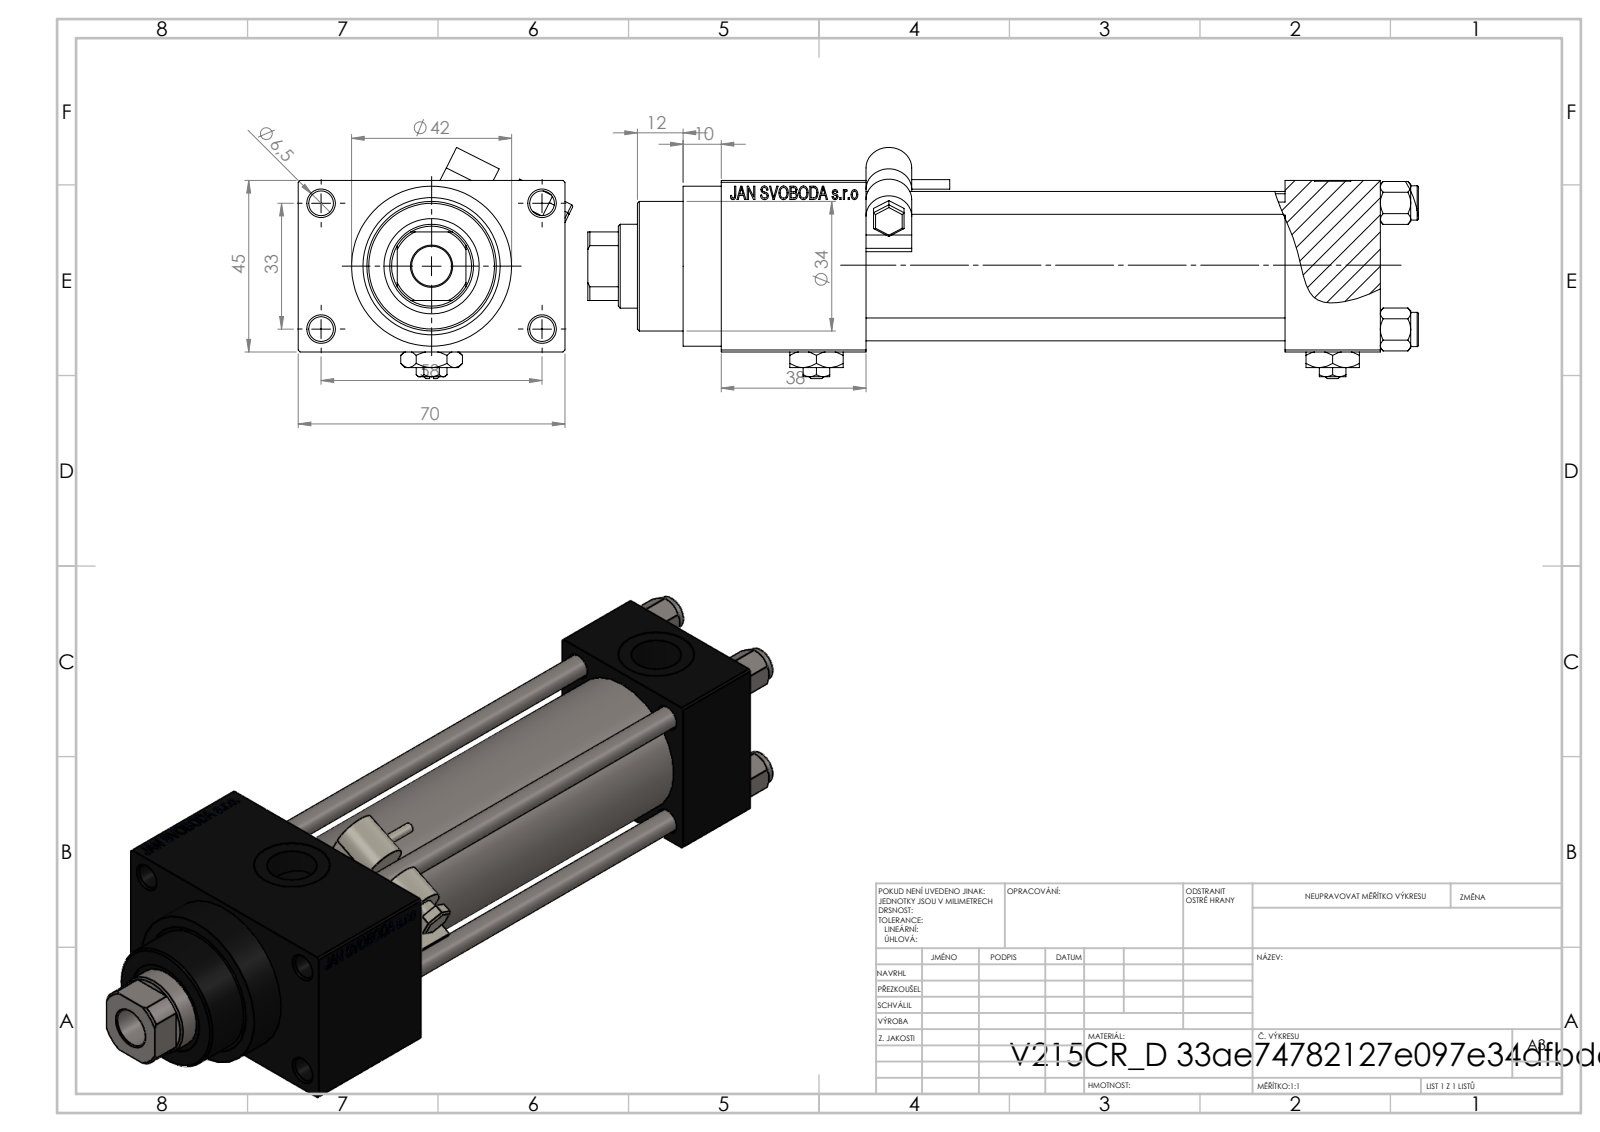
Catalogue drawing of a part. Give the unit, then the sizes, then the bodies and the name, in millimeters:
Units: millimetres
Overall size (bounding box): 218 × 72.03 × 60.66
Round holes (diameter × count): ⌀6 ×4, ⌀6.5 ×4, ⌀7 ×2, ⌀13.16 ×2, ⌀20 ×2, ⌀10.5 ×1, ⌀22 ×1, ⌀24 ×1, ⌀25 ×1, ⌀32 ×1, ⌀33 ×1
Round bosses / shafts (diameter × count): ⌀9 ×4, ⌀42 ×1, ⌀38 ×1, ⌀34 ×1, ⌀5 ×1, ⌀2.5 ×1
Partial cylindrical surfaces — rounded edges, fillets, slot ends (radius × count): R0.5 ×6, R6 ×2, R10.5 ×1
Main face-to-face distances: 45, 25, 12.5, 57.5, 110, 135, 148, 38, 70, 173
Hole centre spacings: 12.4, 23.48, 33.2, 33.37, 35.35, 45.6, 56.35, 33
Volume: 296 110 mm³ · Surface area: 105 076 mm²
Bodies: 14 solids, 1236 faces (560 planar, 114 cylindrical, 562 other)
Part name (STEP PRODUCT): NUT_M5_D; V215CR_D_Body; Zatka_pro_OIL_PORT; MSRF_MSRG1 (+3 more)
STEP written by: SolidWorks 2019 (CONFIG_CONTROL_DESIGN)
